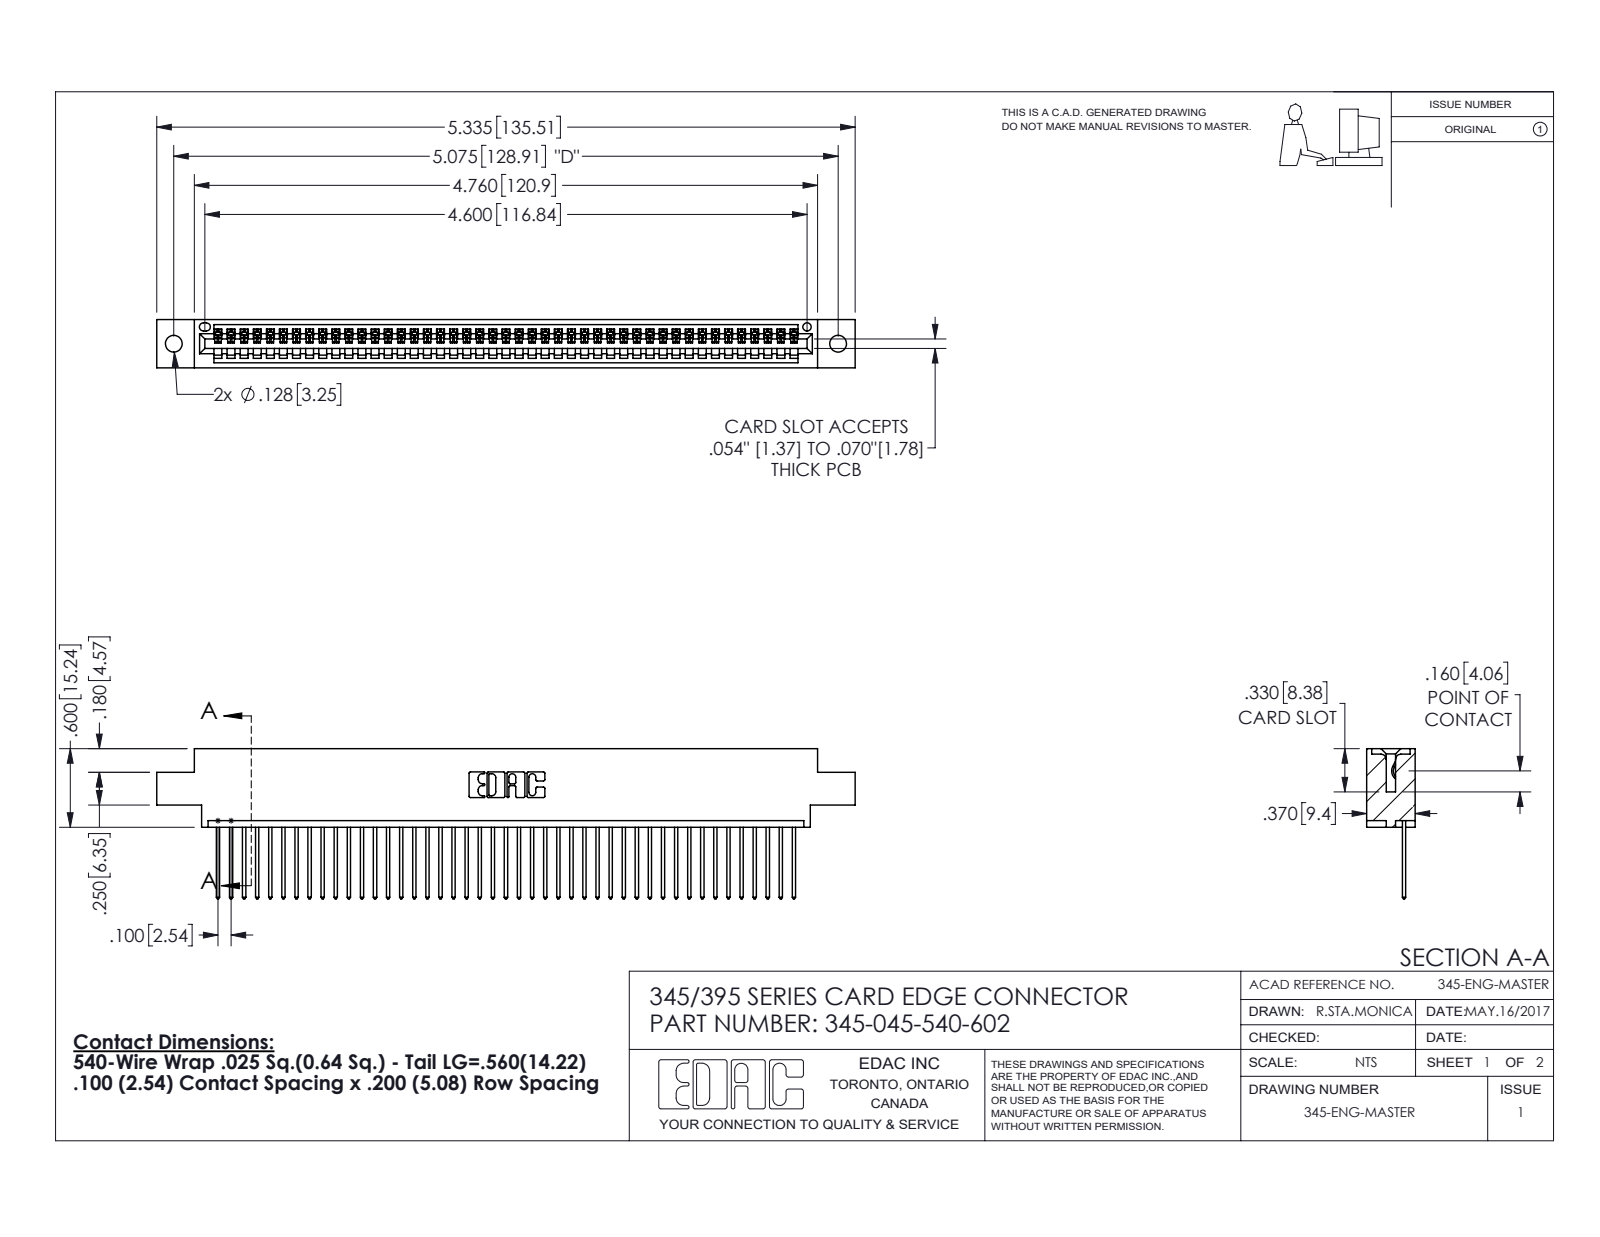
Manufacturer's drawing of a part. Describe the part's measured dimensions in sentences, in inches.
The part is named "345-292-001_345-293-140; 345 Part_0.170 Offset - 0.128 Dia; 345-045-540-602". Its 3-D file was written by "SolidWorks 2016 (CONFIG_CONTROL_DESIGN)". It is 46 solids with 2740 faces: 1884 planar, 856 cylindrical and 0 other. Overall it measures 5.335 by 1.147 by 0.37 inches. Its volume is 0.781 cubic inches and its surface area 26.9 square inches. Round holes: 2 of diameter 0.128, 1 of diameter 0.064. Partial cylindrical surfaces (rounded edges, fillets, slot ends): 90 of radius 0.006, 90 of radius 0.01, 22 of radius 0.01, 6 of radius 0.007, 6 of radius 0.031, 3 of radius 0.026, 2 of radius 0.031, 2 of radius 0.04. The main face-to-face distances are 0.072, 0.298, 0.37, 0.098, 0.272, 0.025, 0.2, 0.225, 0.175, 0.149. The hole center spacings are 0.27, 4.839, 5.075.
